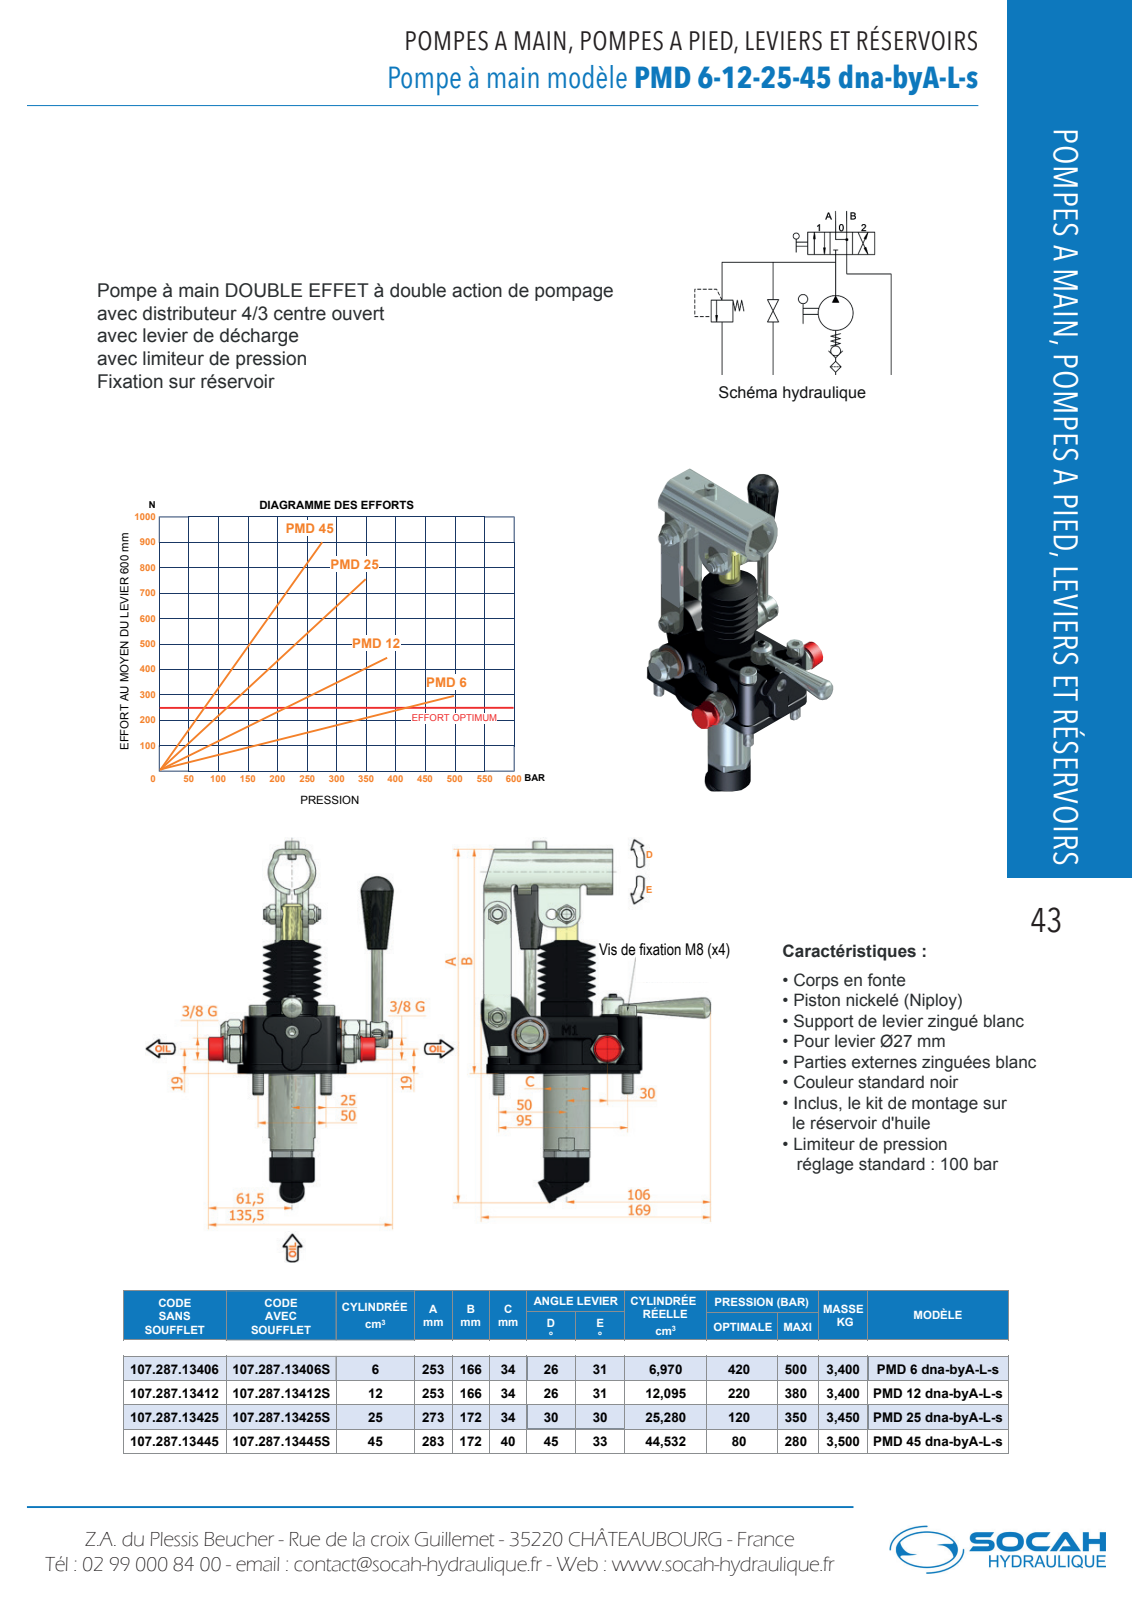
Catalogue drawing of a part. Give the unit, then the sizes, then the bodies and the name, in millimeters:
Units: millimetres
Overall size (bounding box): 277.85 × 169 × 136.22
Round holes (diameter × count): ⌀8 ×7, ⌀5 ×4, ⌀14 ×4, ⌀4.92 ×3, ⌀4 ×1, ⌀7.5 ×1, ⌀9 ×1, ⌀10 ×1, ⌀10.5 ×1, ⌀13.5 ×1, ⌀16 ×1, ⌀17 ×1
Round bosses / shafts (diameter × count): ⌀13 ×4, ⌀12 ×4, ⌀8.5 ×4, ⌀8 ×4, ⌀6 ×4, ⌀20 ×3, ⌀18 ×3, ⌀16 ×3
Partial cylindrical surfaces — rounded edges, fillets, slot ends (radius × count): R1 ×30, R0.2 ×24, R0.1 ×16, R5 ×16, R2 ×14, R3 ×9, R8 ×9, R0.36 ×6
Main face-to-face distances: 4, 20, 5, 37, 16, 2, 42, 24, 44, 1
Hole centre spacings: 24.35, 24.76, 25.5, 27.31, 31.91, 34, 47.89, 50
Volume: 354 223 mm³ · Surface area: 162 425 mm²
Bodies: 18 solids, 1613 faces (737 planar, 365 cylindrical, 511 other)
Part name (STEP PRODUCT): 6056.0048.10.50 Derivazione 2
STEP written by: Autodesk Inventor 2013 (AUTOMOTIVE_DESIGN)
